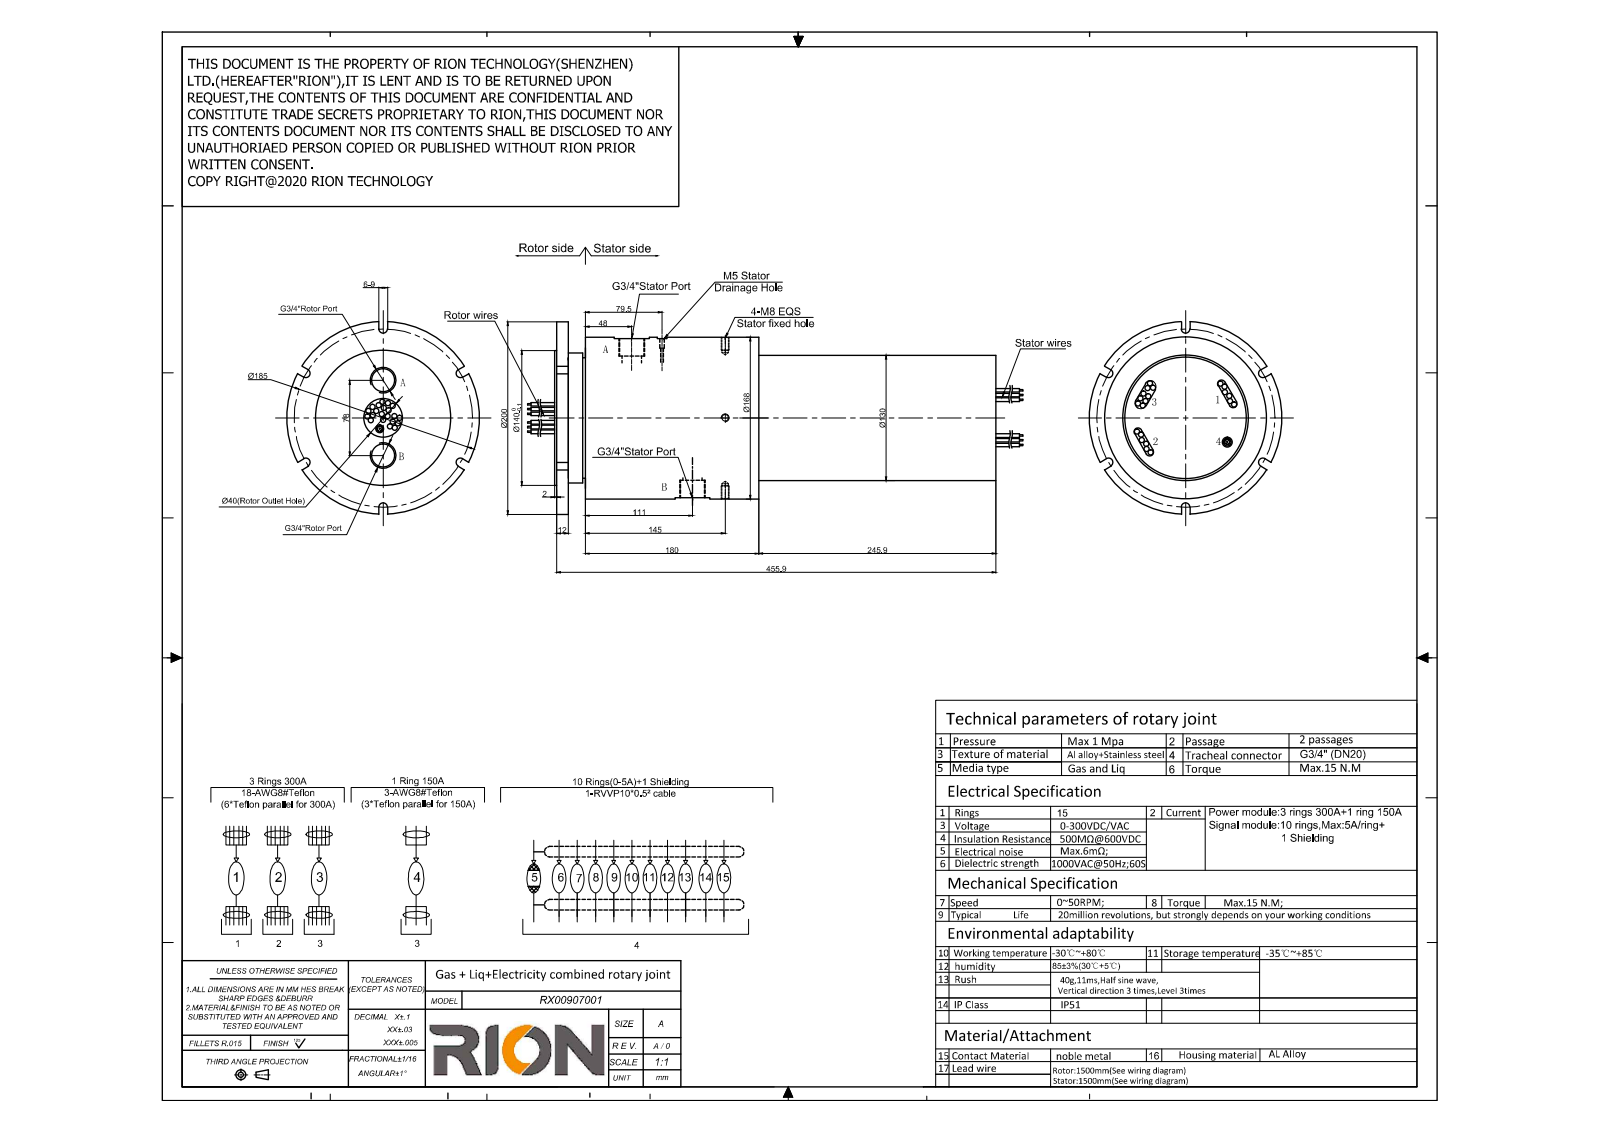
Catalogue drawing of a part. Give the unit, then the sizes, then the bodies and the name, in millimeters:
Units: millimetres
Overall size (bounding box): 517.4 × 200 × 199.8
Round holes (diameter × count): ⌀24.5 ×4, ⌀6.8 ×2, ⌀4.2 ×1, ⌀40 ×1, ⌀126 ×1
Round bosses / shafts (diameter × count): ⌀5.3 ×41, ⌀8 ×2, ⌀200 ×1, ⌀168 ×1, ⌀140 ×1, ⌀135 ×1, ⌀130 ×1, ⌀125.6 ×1
Partial cylindrical surfaces — rounded edges, fillets, slot ends (radius × count): R4.5 ×6, R4 ×4, R6 ×2, R2.65 ×1
Main face-to-face distances: 12, 2, 14, 457.9, 455.9, 443.9, 30, 32, 18, 425.9
Hole centre spacings: 31.5, 39, 34, 63, 65.5, 78, 97
Volume: 7 849 000 mm³ · Surface area: 333 856 mm²
Bodies: 22 solids, 274 faces (110 planar, 146 cylindrical, 18 other)
Part name (STEP PRODUCT): RX00907001
STEP written by: SolidWorks 2014 (AUTOMOTIVE_DESIGN)
